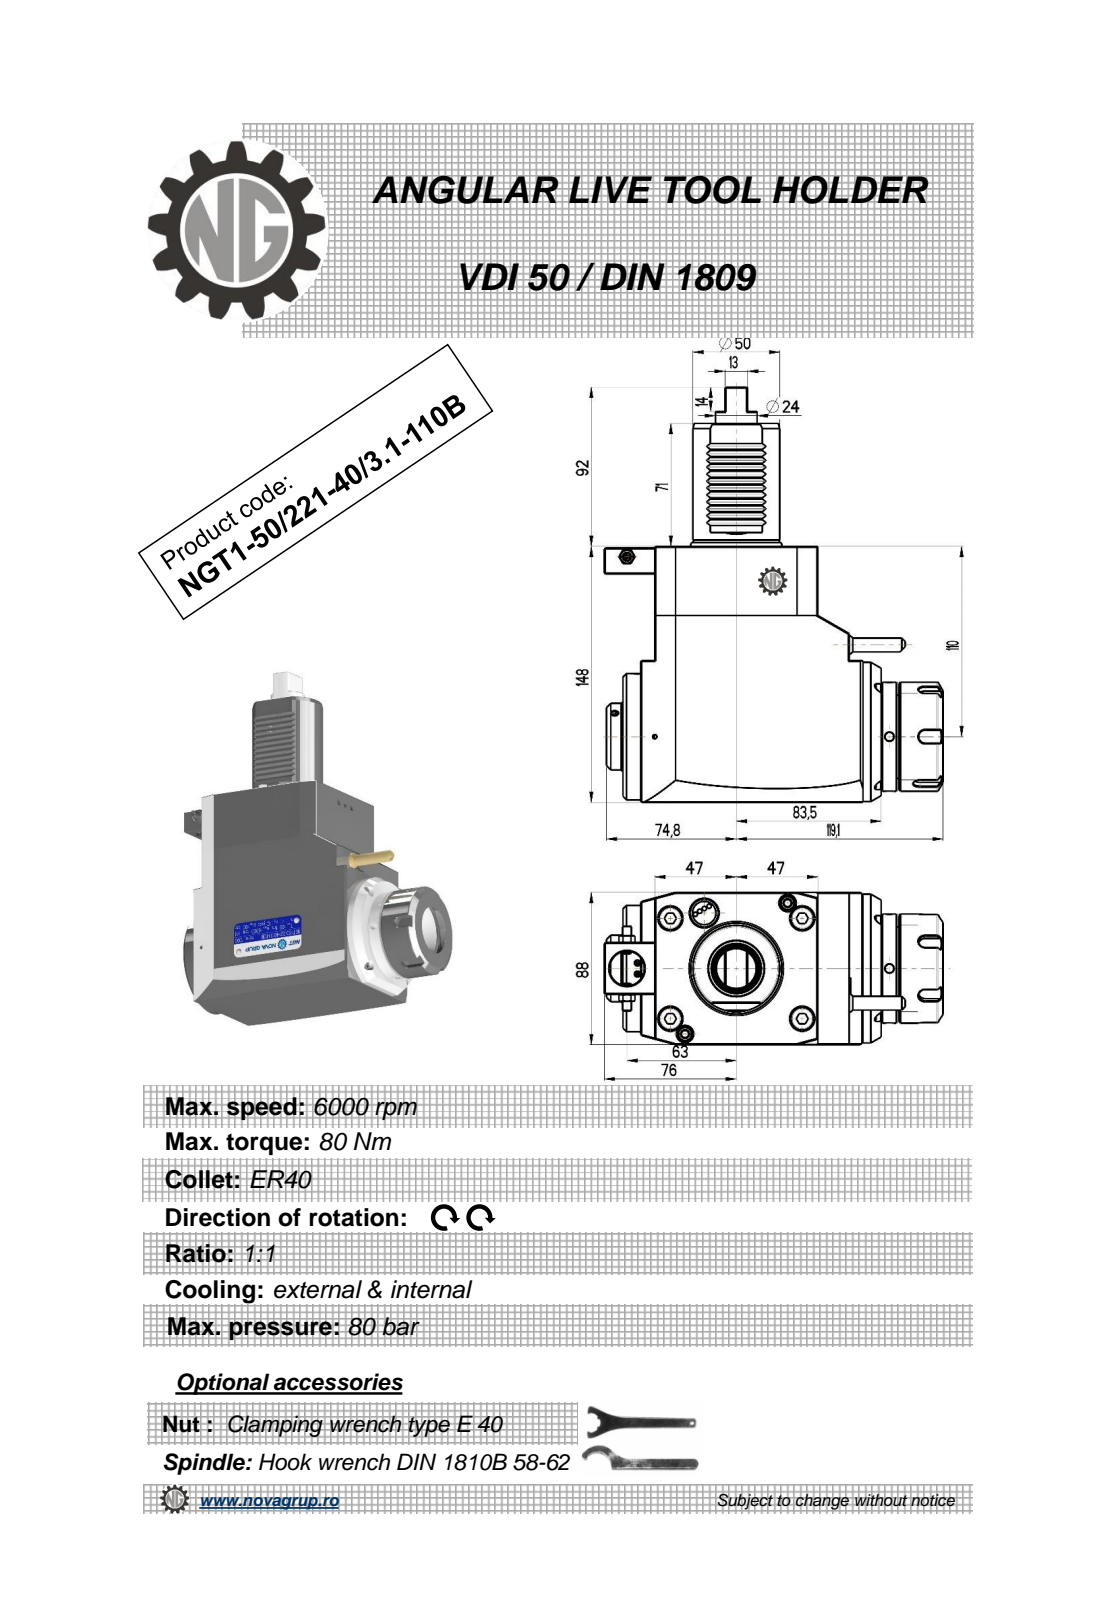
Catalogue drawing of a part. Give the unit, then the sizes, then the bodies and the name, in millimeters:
Units: millimetres
Overall size (bounding box): 240 × 195.1 × 88
Round holes (diameter × count): ⌀5 ×3, ⌀3.8 ×2, ⌀4 ×2, ⌀3 ×1, ⌀9.5 ×1, ⌀20 ×1, ⌀33.5 ×1
Round bosses / shafts (diameter × count): ⌀86 ×1, ⌀73 ×1, ⌀63 ×1, ⌀51 ×1, ⌀50 ×1, ⌀38.5 ×1, ⌀24 ×1, ⌀10 ×1
Partial cylindrical surfaces — rounded edges, fillets, slot ends (radius × count): R0.26 ×12, R0.3 ×12, R0.2 ×6, R3.75 ×5, R0.8 ×2
Main face-to-face distances: 88, 148, 8, 94, 130.5, 36.5, 120, 18.3, 112.3, 148.8
Hole centre spacings: 9, 101.9, 18, 49.73, 52.46, 56.51, 56.65, 101.5
Volume: 1 844 000 mm³ · Surface area: 115 317 mm²
Bodies: 1 solid, 435 faces (210 planar, 100 cylindrical, 125 other)
Part name (STEP PRODUCT): NGT1_50_221_40_3_1_110B
STEP written by: PRO/ENGINEER BY PARAMETRIC TECHNOLOGY CORPORATION, 2010280 (CONFIG_CONTROL_DESIGN)
